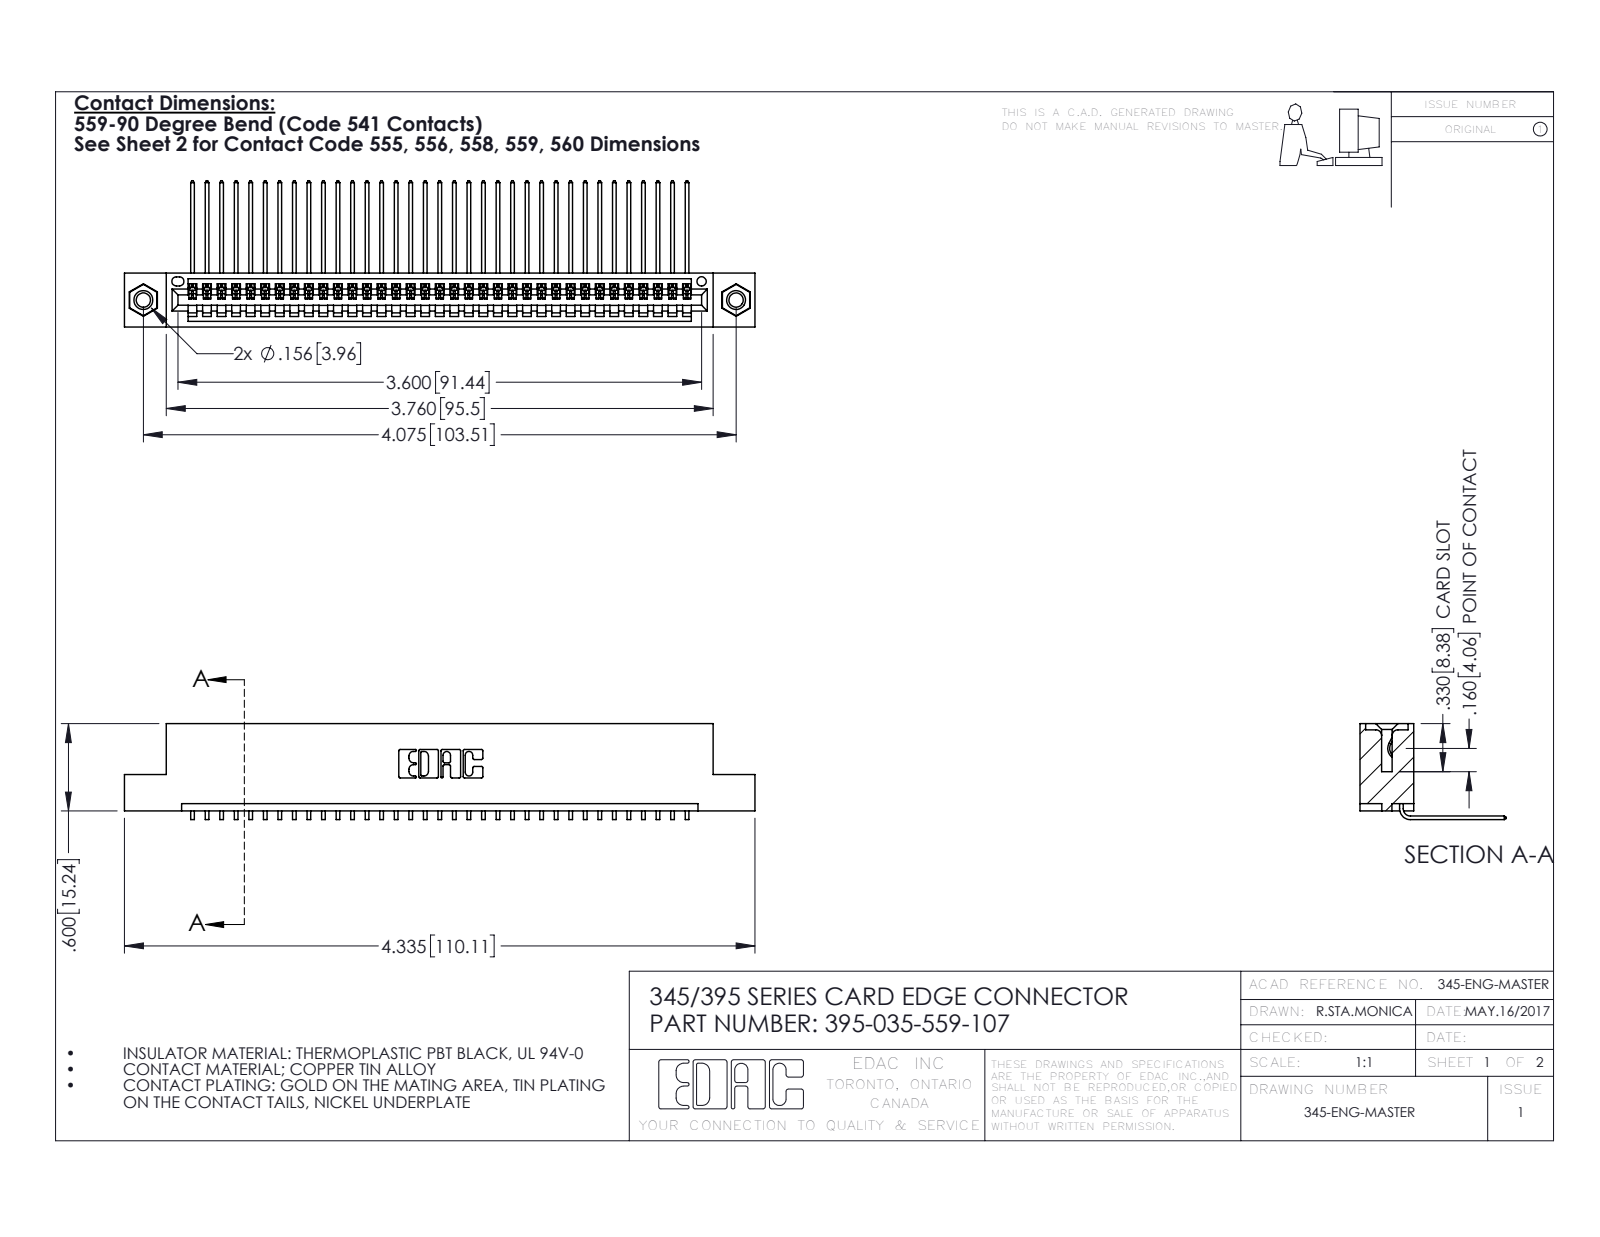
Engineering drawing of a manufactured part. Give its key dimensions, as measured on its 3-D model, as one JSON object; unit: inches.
{"part_name": "345-292-001_558 559 Tail - 1; 345 Part_Flush Mounting Lugs - 0.156 Dia-TI; 395-035-559-107; 345-250-001_345-250-005-103", "step_written_by": "SolidWorks 2016 (CONFIG_CONTROL_DESIGN)", "units": "inches", "bodies": {"solids": 38, "faces": 2286, "planar": 1582, "cylindrical": 688, "other": 16}, "overall_size": [4.335, 1.005, 0.659], "volume_in3": 0.641, "surface_area_in2": 22.6, "round_holes": [[0.098, 2], [0.125, 2], [0.156, 2], [0.064, 1]], "round_bosses_or_shafts": [[0.155, 2]], "partial_cylinders_radius": [[0.006, 70], [0.01, 22], [0.007, 6], [0.031, 6], [0.026, 3], [0.031, 2], [0.04, 2], [0.014, 1]], "face_to_face_distances": [0.072, 0.298, 0.37, 0.2, 0.098, 0.272, 0.025, 0.225, 0.149, 0.072], "hole_center_spacings": [0.27, 3.839, 4.075]}
